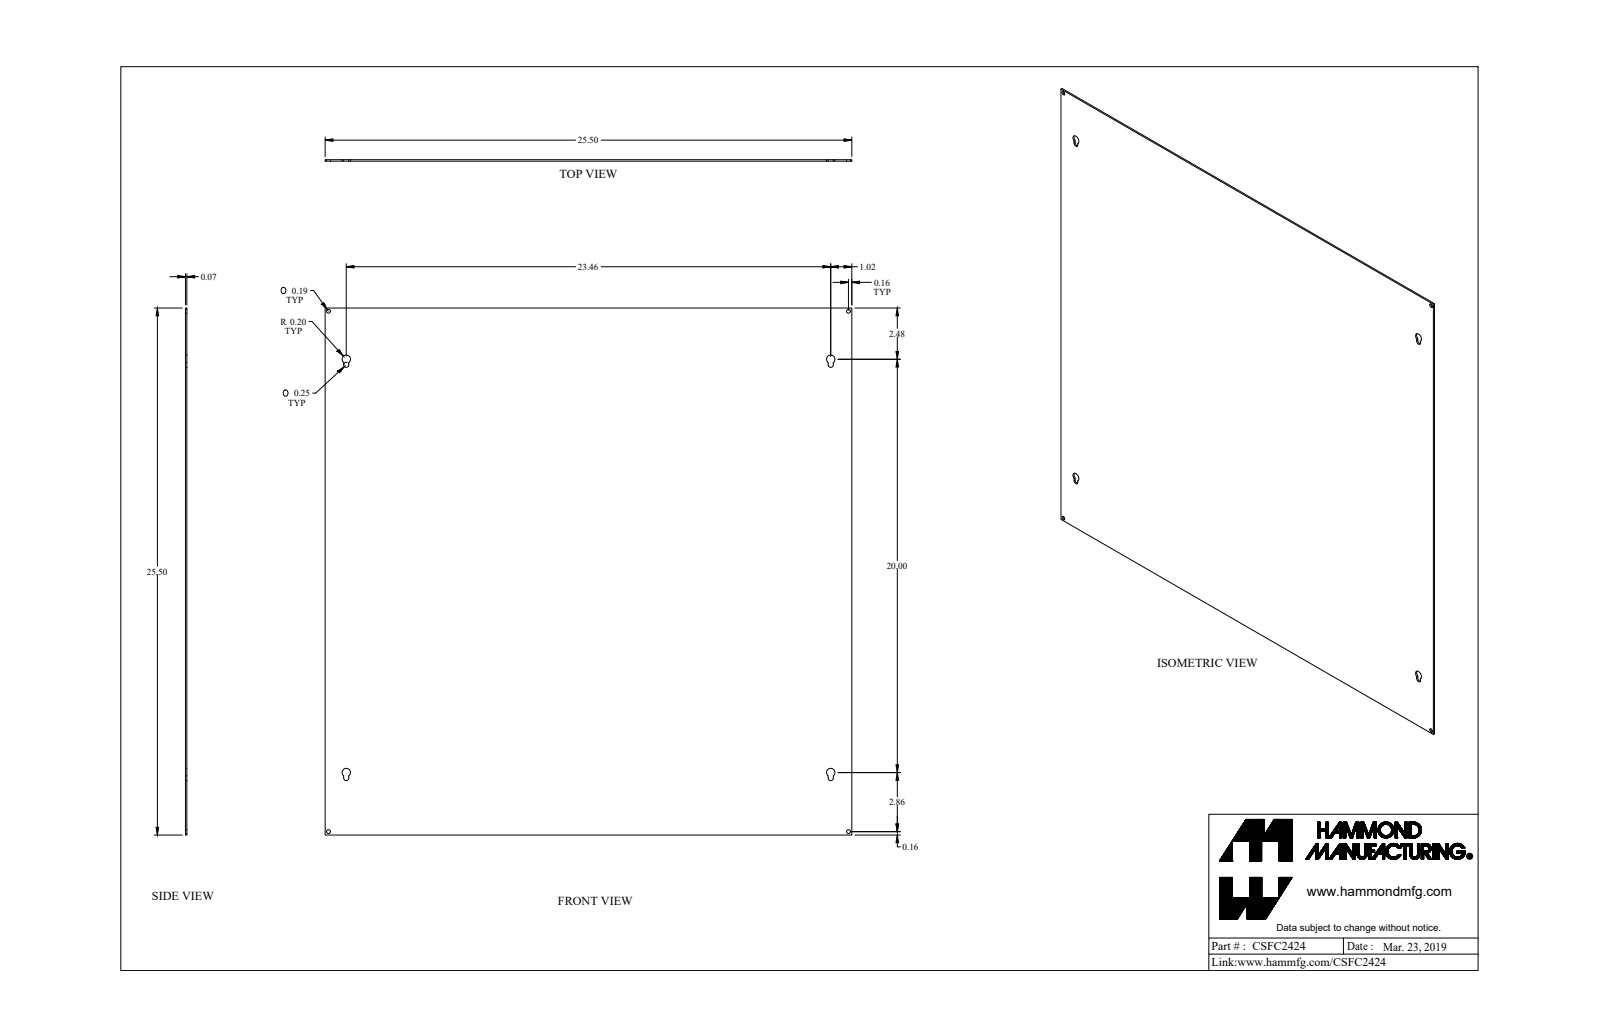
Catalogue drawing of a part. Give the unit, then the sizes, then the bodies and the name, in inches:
Units: inches
Overall size (bounding box): 25.5 × 25.5 × 0.072
Round holes (diameter × count): ⌀0.188 ×4
Partial cylindrical surfaces — rounded edges, fillets, slot ends (radius × count): R0.125 ×4, R0.203 ×4
Main face-to-face distances: 0.072, 25.5, 1.145, 24.355, 0.895, 24.605, 23.46, 0.25, 23.21, 23.71
Hole centre spacings: 25.18, 35.61
Volume: 46.76 in³ · Surface area: 1 307 in²
Bodies: 1 solid, 38 faces (14 planar, 24 cylindrical, 0 other)
Part name (STEP PRODUCT): CSFC2424_Default
STEP written by: SolidWorks 2019 (CONFIG_CONTROL_DESIGN)
